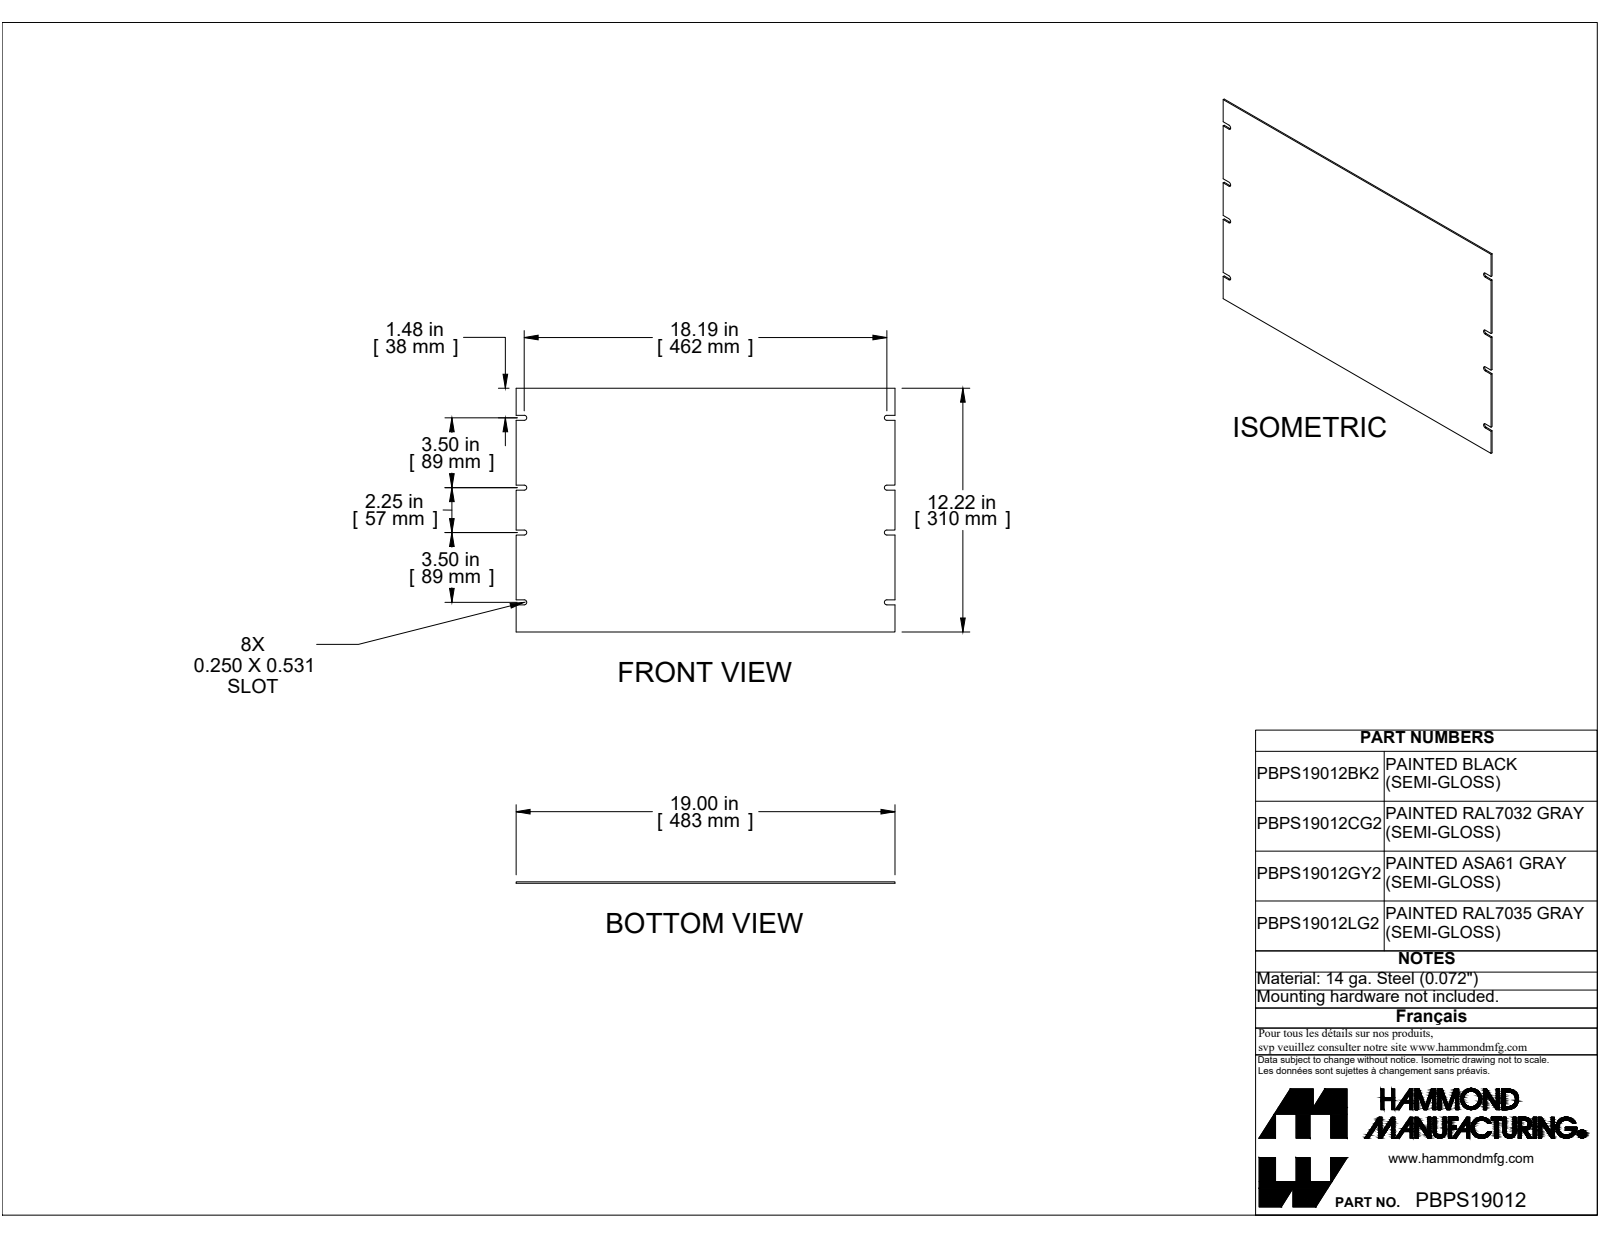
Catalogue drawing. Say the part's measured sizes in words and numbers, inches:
The part is named "PBPS19012GY2". Its 3-D file was written by "SolidWorks 2019 (CONFIG_CONTROL_DESIGN)". It is 1 solid with 38 faces: 30 planar, 8 cylindrical and 0 other. Overall it measures 19 by 12.218 by 0.072 inches. Its volume is 16.64 cubic inches and its surface area 467.3 square inches. Partial cylindrical surfaces (rounded edges, fillets, slot ends): 8 of radius 0.125. The main face-to-face distances are 0.072, 12.218, 19, 0.25, 5.75, 3.5, 4.859, 7.359, 5.109, 7.109.
